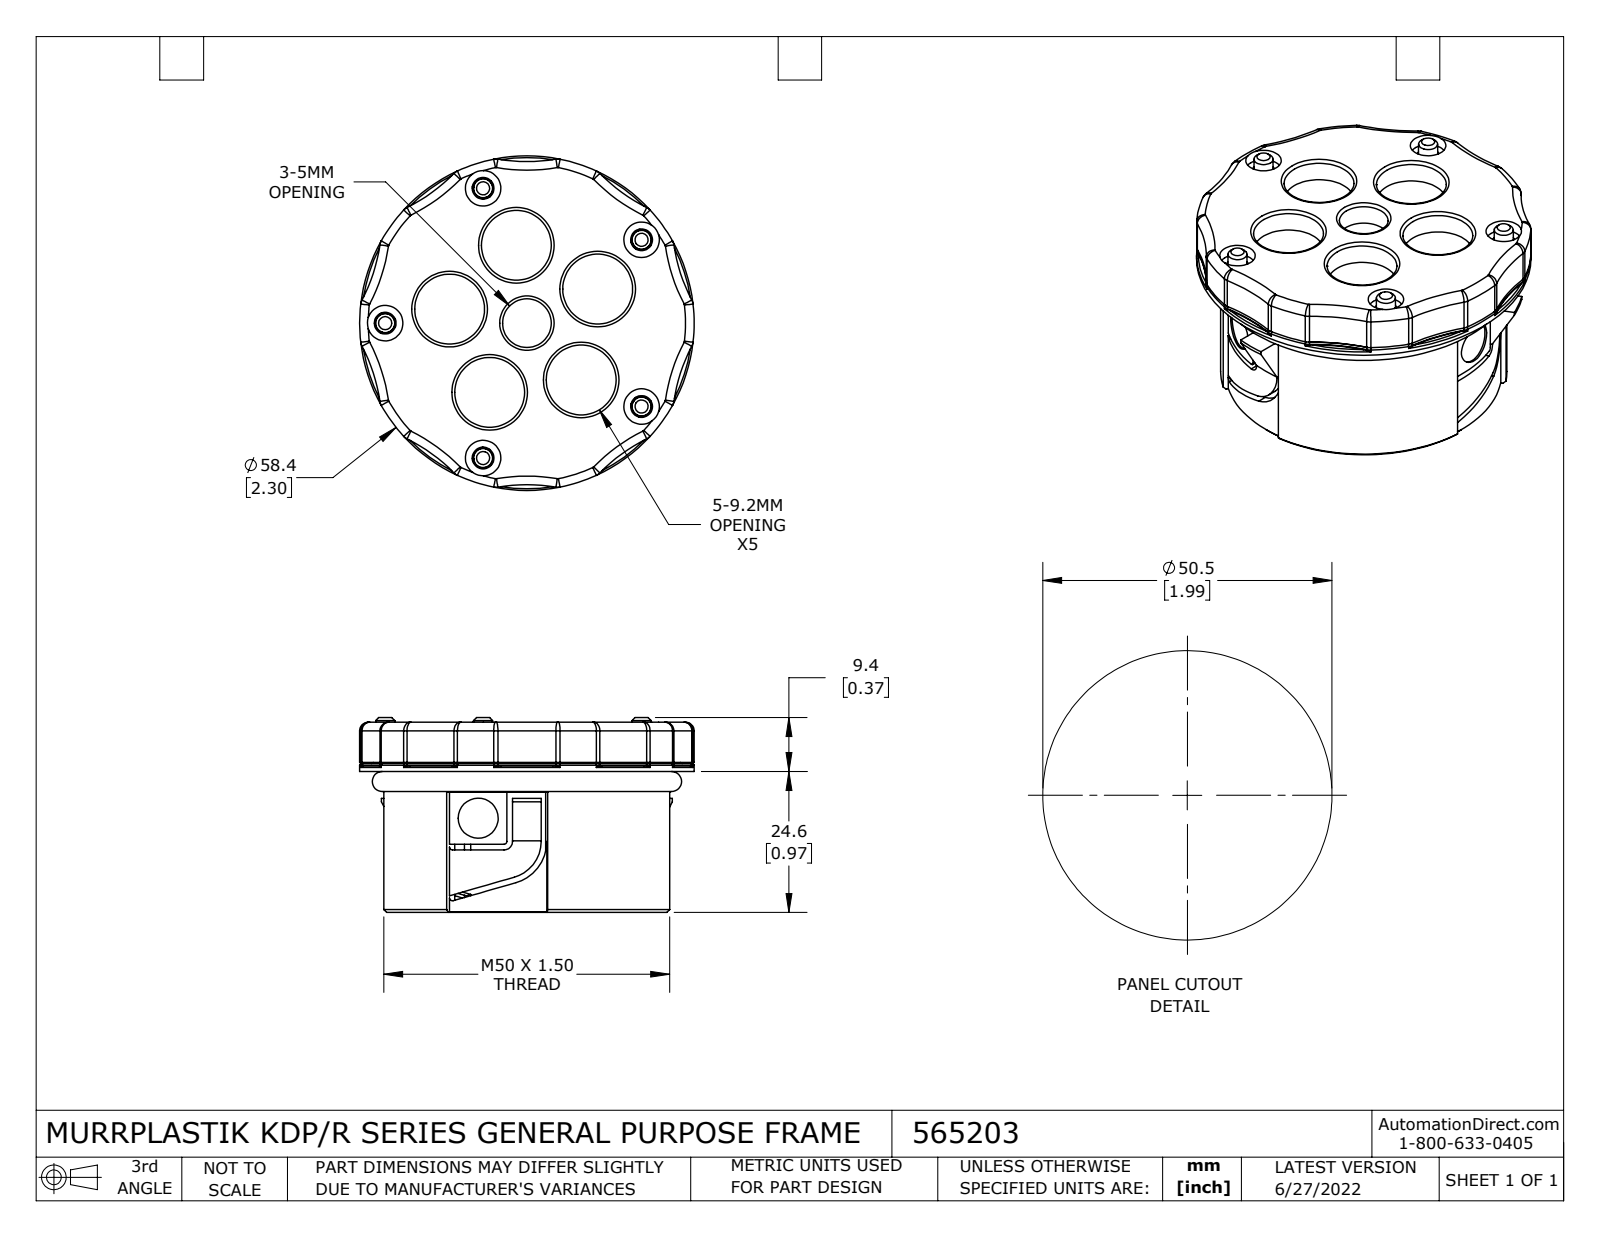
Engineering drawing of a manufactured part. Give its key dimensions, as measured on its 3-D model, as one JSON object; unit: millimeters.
{"part_name": "565203", "step_written_by": "SolidWorks 2021 (CONFIG_CONTROL_DESIGN)", "units": "millimeters", "bodies": {"solids": 6, "faces": 502, "planar": 90, "cylindrical": 203, "other": 209}, "overall_size": [58.4, 58.4, 34], "volume_mm3": 30772, "surface_area_mm2": 31191, "round_holes": [[3.8, 8], [6.2, 5], [12.2, 5], [7, 3], [8.5, 1], [43.4, 1], [45, 1], [54.4, 1]], "round_bosses_or_shafts": [[58.4, 1], [53.4, 1], [51, 1], [50, 1], [48.7, 1], [46, 1], [44.2, 1], [41.71, 1]], "partial_cylinders_radius": [[2, 20], [30, 10], [0.3, 6], [0.5, 5], [1.5, 3], [6.5, 3], [7.5, 3], [1.75, 2]], "face_to_face_distances": [1.75, 3.5, 4, 7.5, 5.75, 8.2, 4.7, 6.45, 12.2, 1.1], "hole_center_spacings": [24.75, 37.58, 11.52, 35.64, 13.72, 16.13, 19.75, 21.89]}
